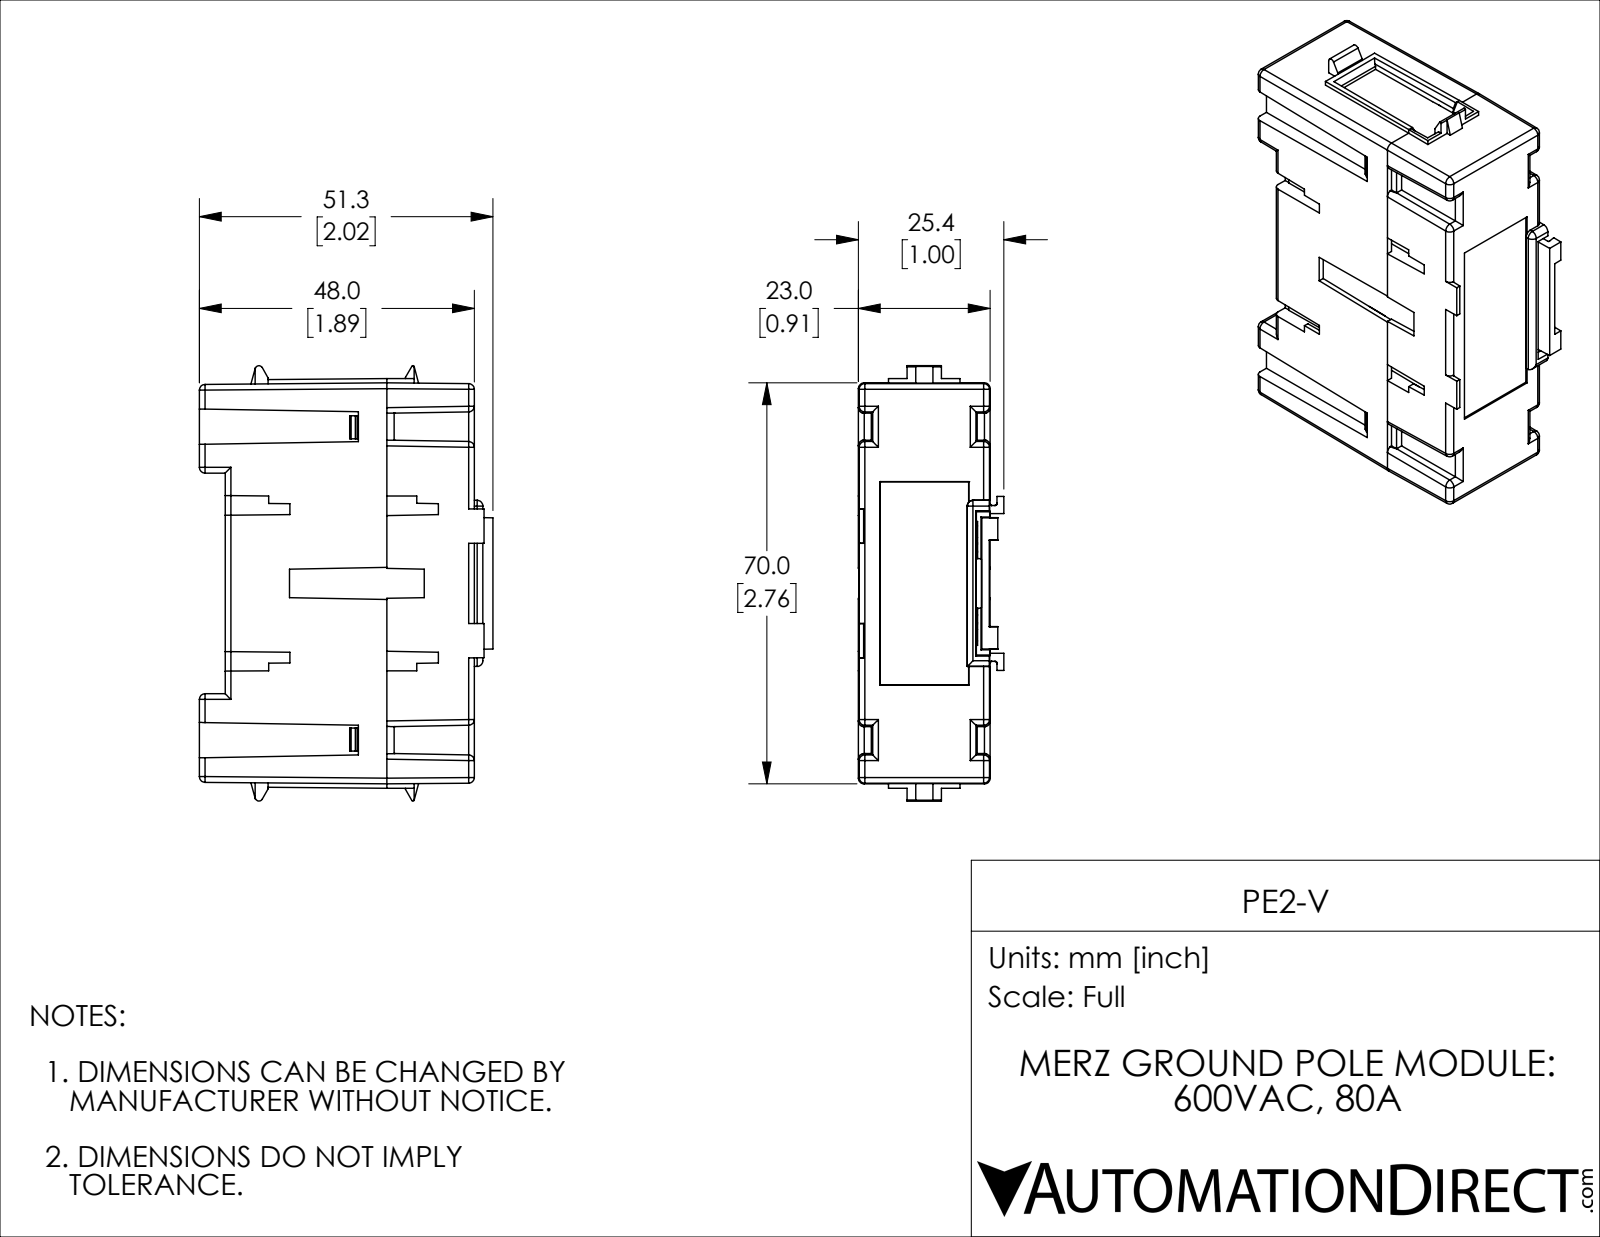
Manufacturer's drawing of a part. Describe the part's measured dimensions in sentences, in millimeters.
The part is named "PE2-V". Its 3-D file was written by "SolidWorks 2019 (AUTOMOTIVE_DESIGN)". It is 1 solid with 672 faces: 559 planar, 81 cylindrical and 32 other. Overall it measures 76 by 51.3 by 25.4 millimeters. Its volume is 63 710 cubic millimeters and its surface area 24 550 square millimeters. Partial cylindrical surfaces (rounded edges, fillets, slot ends): 42 of radius 1, 6 of radius 0.5, 4 of radius 0.3, 3 of radius 0.2, 2 of radius 0.6. The main face-to-face distances are 1, 23, 17.2, 22, 43.2, 18.7, 42.9, 4.8, 47.7, 48.
